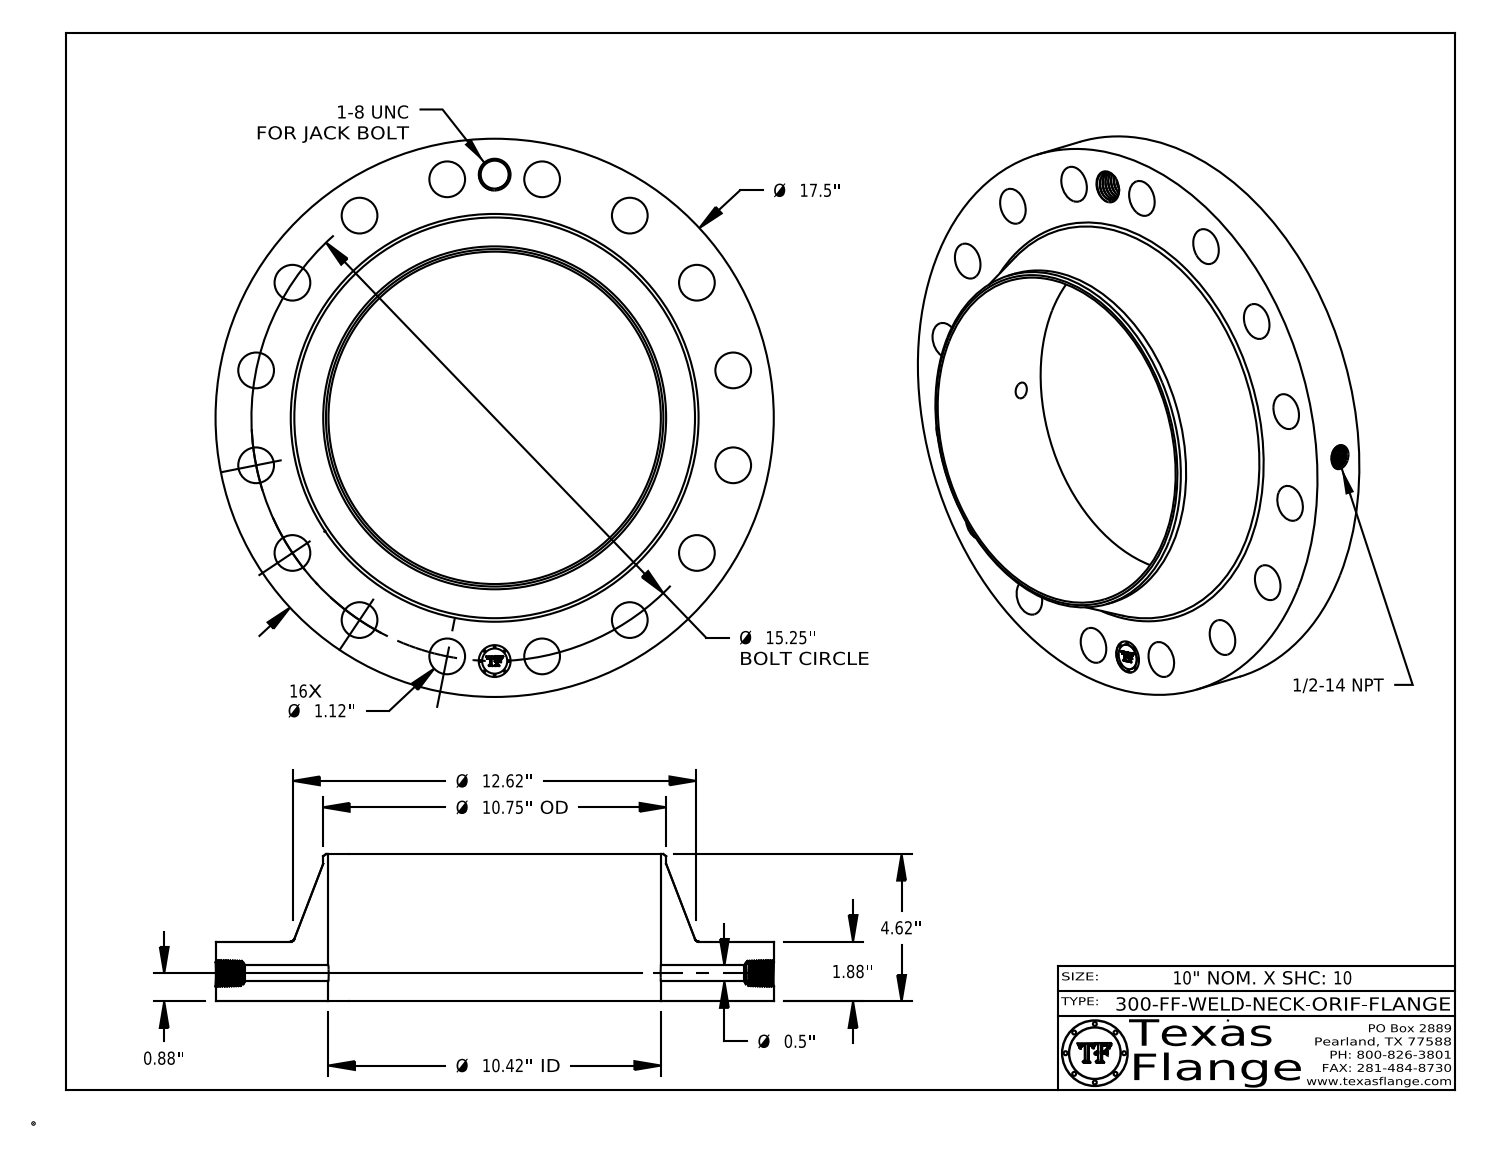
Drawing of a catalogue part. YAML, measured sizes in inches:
part_name: "300-FF-WELD-NECK"
step_written_by: "CATIA V5 STEP AP214 (AUTOMOTIVE_DESIGN)"
units: inches
bodies: {solids: 1, faces: 784, planar: 368, cylindrical: 107, other: 309}
overall_size: [17.5, 17.5, 4.62]
volume: 314.8
surface_area: 729.9
round_holes:
  - {diameter: 1.12, count: 16}
  - {diameter: 0.5, count: 1}
  - {diameter: 0.672, count: 1}
  - {diameter: 0.875, count: 1}
  - {diameter: 1, count: 1}
  - {diameter: 10.42, count: 1}
round_bosses_or_shafts:
  - {diameter: 0.061, count: 8}
  - {diameter: 17.5, count: 1}
  - {diameter: 10.75, count: 1}
  - {diameter: 0.788, count: 1}
face_to_face_distances: [1.88, 4.62, 2.74, 0.015, 1.865, 2.755, 0.298, 0.292, 0.054, 0.248]
hole_center_spacings: [5.836, 7.625, 10.783, 14.089, 14.957, 2.975, 2.975, 8.472]
